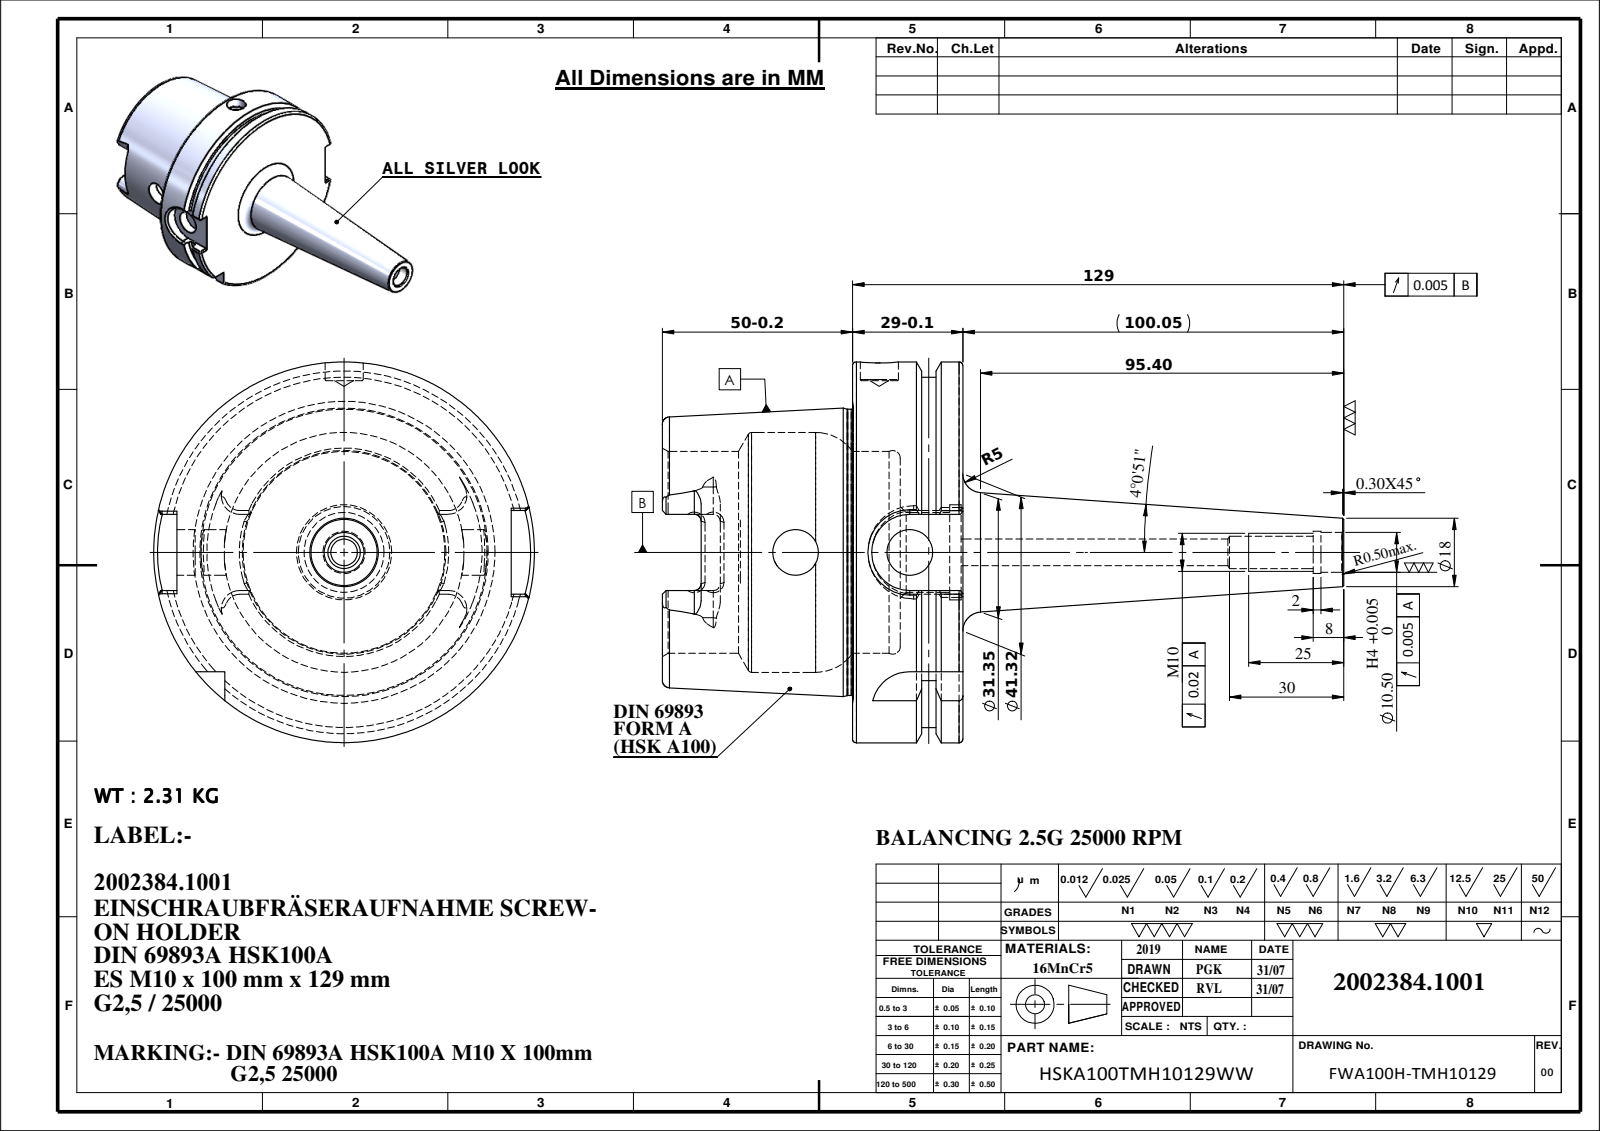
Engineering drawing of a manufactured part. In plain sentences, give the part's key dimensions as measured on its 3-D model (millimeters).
The part is named "91100A-ES8M10100; HSKA100TMH10129WW". Its 3-D file was written by "SolidWorks 2018 (CONFIG_CONTROL_DESIGN)". It is 1 solid with 174 faces: 50 planar, 52 cylindrical and 72 other. Overall it measures 179 by 100 by 100 millimeters. Its volume is 299 868 cubic millimeters and its surface area 59 325 square millimeters. Round holes: 2 of diameter 12, 1 of diameter 7, 1 of diameter 8.5, 1 of diameter 10, 1 of diameter 10.5, 1 of diameter 11.1, 1 of diameter 21, 1 of diameter 25, 1 of diameter 53, 1 of diameter 63. Round bosses or shafts: 1 of diameter 100, 1 of diameter 92, 1 of diameter 75.16. Partial cylindrical surfaces (rounded edges, fillets, slot ends): 6 of radius 1.8, 4 of radius 4.88, 2 of radius 10, 1 of radius 11. The main face-to-face distances are 28.95, 12.5, 16.45, 50, 62.5, 78.95, 78.5, 28.5, 16, 0.45. The hole center spacings are 30.
